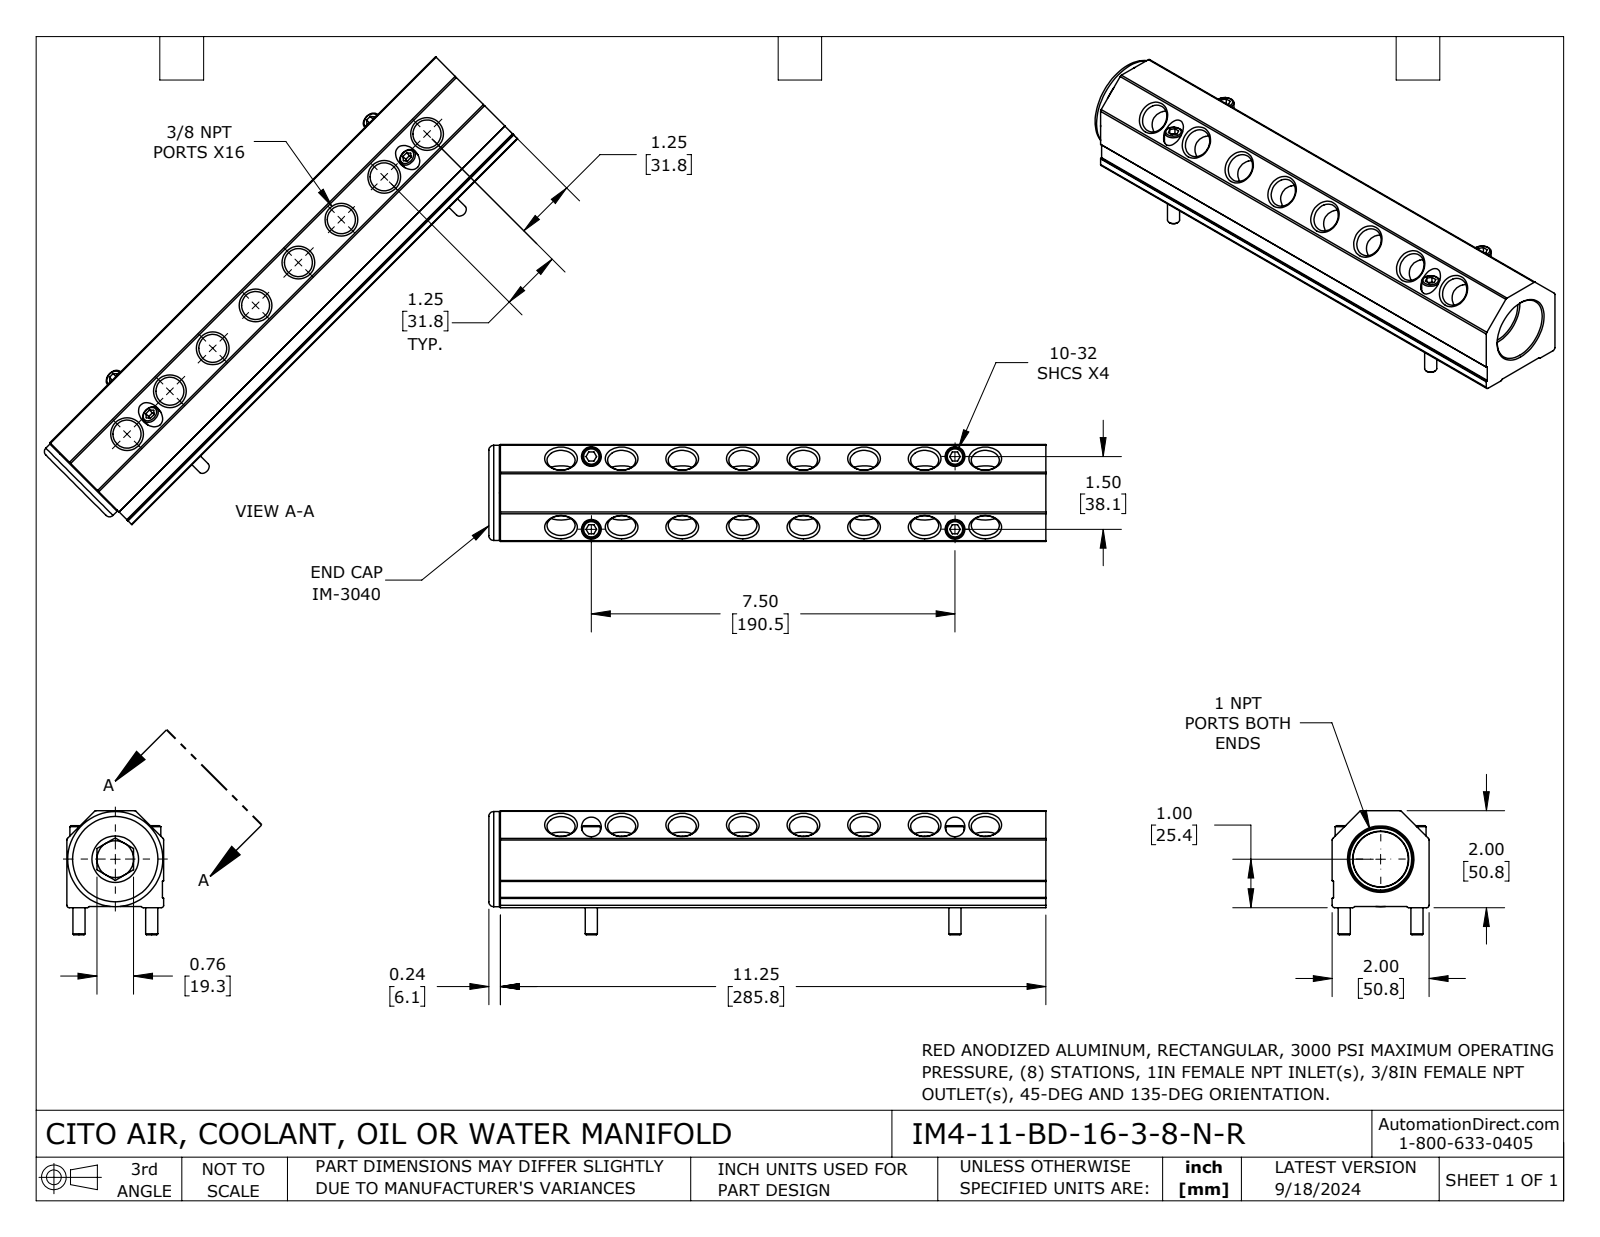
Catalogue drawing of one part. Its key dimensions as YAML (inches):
part_name: "IM4-11-BD-16-3-8-N-R"
step_written_by: "SolidWorks 2023 (CONFIG_CONTROL_DESIGN)"
units: inches
bodies: {solids: 6, faces: 245, planar: 81, cylindrical: 90, other: 74}
overall_size: [11.49, 2.56, 2]
volume: 27.69
surface_area: 158.4
round_holes:
  - {diameter: 0.578, count: 16}
  - {diameter: 0.266, count: 4}
  - {diameter: 0.406, count: 4}
  - {diameter: 0.758, count: 1}
  - {diameter: 1.156, count: 1}
  - {diameter: 1.637, count: 1}
round_bosses_or_shafts:
  - {diameter: 0.375, count: 4}
  - {diameter: 0.25, count: 4}
  - {diameter: 1.96, count: 1}
  - {diameter: 1.359, count: 1}
  - {diameter: 1.293, count: 1}
  - {diameter: 1.14, count: 1}
partial_cylinders:
  - {radius: 0.05, count: 8}
  - {radius: 0.01, count: 4}
face_to_face_distances: [2, 1.975, 0.025, 0.028, 1.972, 11.25, 0.24, 11.49, 0.764, 0.524]
hole_center_spacings: [1.25, 2.5, 3.75, 5, 6.25, 7.5, 1.5, 7.648]
